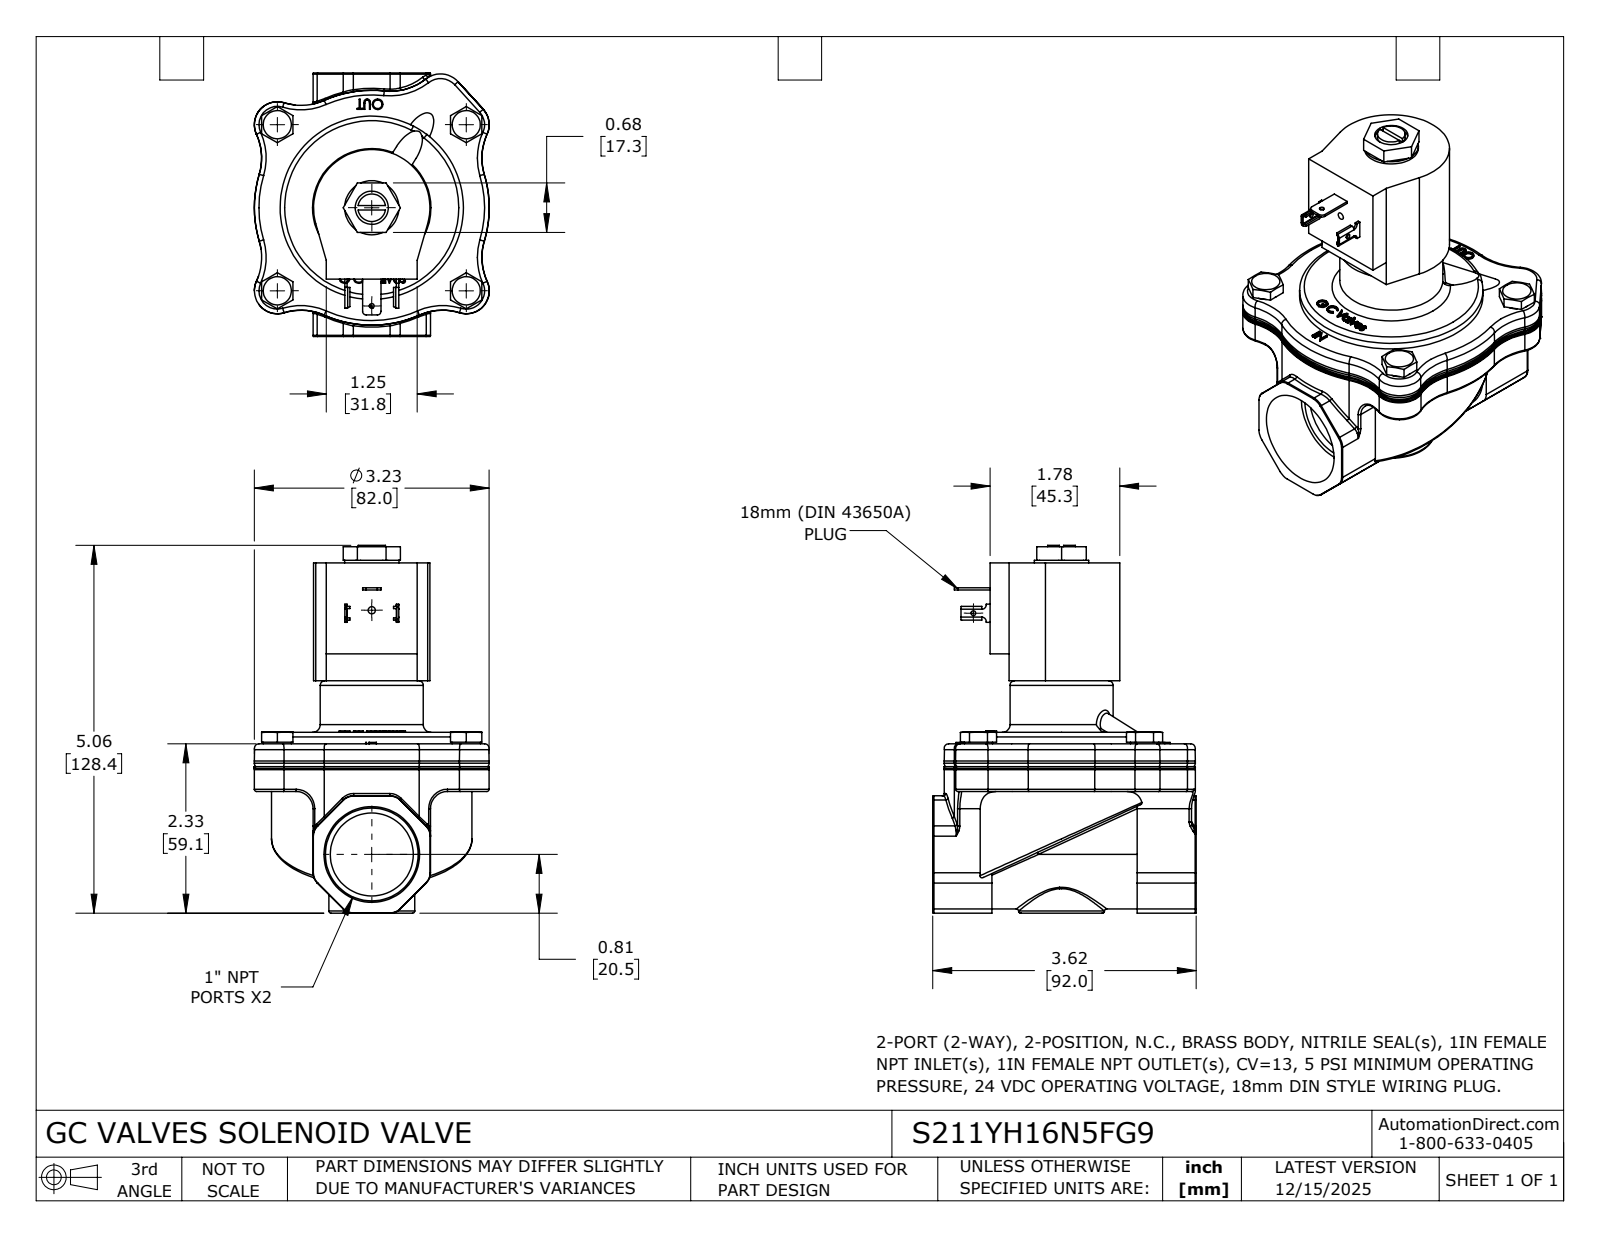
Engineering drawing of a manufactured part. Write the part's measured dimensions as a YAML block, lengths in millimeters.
part_name: "S211YH16N5FG9"
step_written_by: "SolidWorks 2024 (CONFIG_CONTROL_DESIGN)"
units: millimeters
bodies: {solids: 1, faces: 671, planar: 220, cylindrical: 172, other: 279}
overall_size: [128.4, 92, 82.1]
volume: 322300
surface_area: 44200
round_holes:
  - {diameter: 1.7, count: 1}
  - {diameter: 1.7, count: 1}
  - {diameter: 2.5, count: 1}
  - {diameter: 11.6, count: 1}
  - {diameter: 29, count: 1}
round_bosses_or_shafts:
  - {diameter: 9.9, count: 4}
  - {diameter: 64, count: 1}
  - {diameter: 36, count: 1}
  - {diameter: 30, count: 1}
  - {diameter: 18.9, count: 1}
  - {diameter: 9.7, count: 1}
partial_cylinders:
  - {radius: 0.8, count: 24}
  - {radius: 20, count: 24}
  - {radius: 8, count: 12}
  - {radius: 5, count: 8}
  - {radius: 0.2, count: 4}
  - {radius: 1, count: 4}
  - {radius: 1.3, count: 2}
  - {radius: 1.5, count: 2}
face_to_face_distances: [4, 16.6, 20.6, 79.8, 63.1, 59.2, 63.1, 59.1, 42.5, 122.3]
hole_center_spacings: [34.3, 85.2]
